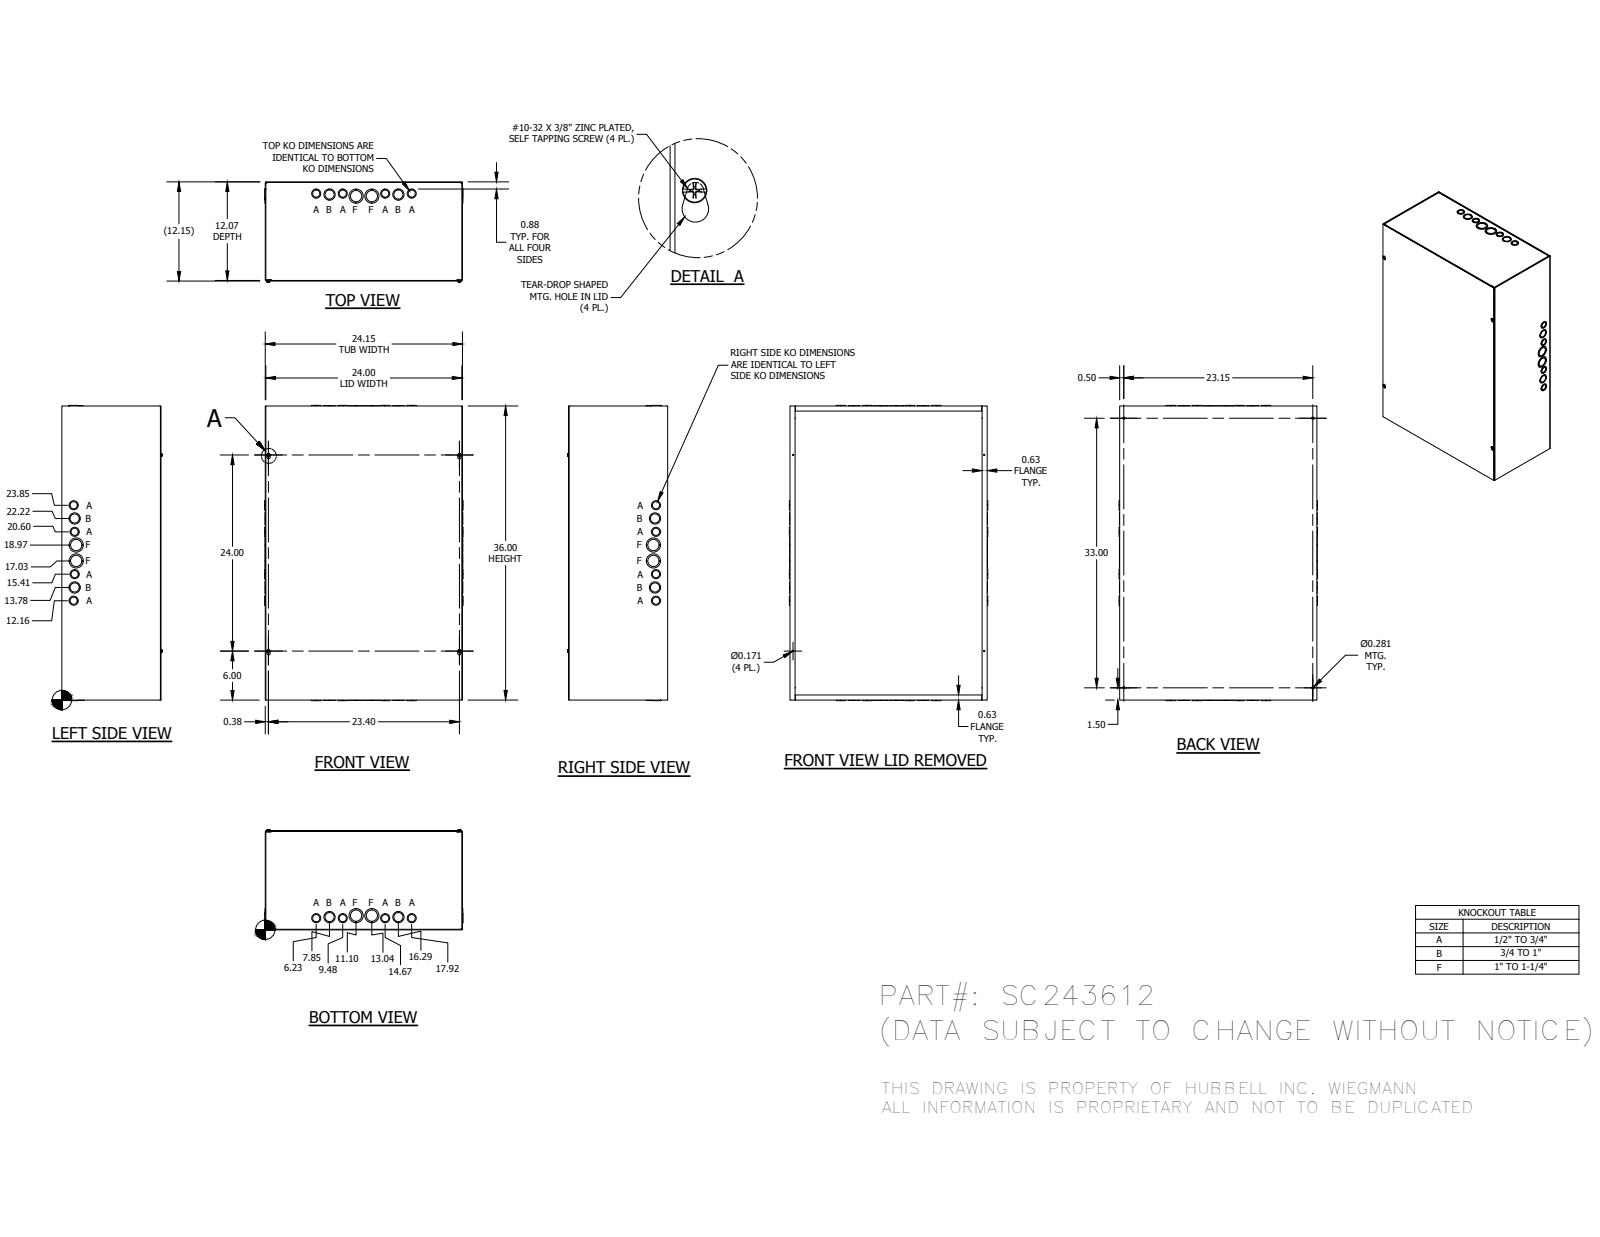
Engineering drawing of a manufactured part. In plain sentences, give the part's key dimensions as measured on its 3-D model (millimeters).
The part is named "SC243612BLR; SC2412TB; SC2436LPA; 37214 (+1 more)". Its 3-D file was written by "Autodesk Inventor 2014 (AUTOMOTIVE_DESIGN)". It is 37 solids with 1219 faces: 899 planar, 236 cylindrical and 84 other. Overall it measures 918.16 by 617.12 by 311.91 millimeters. Round holes: 14 of diameter 28.57, 10 of diameter 22.22, 8 of diameter 34.92, 4 of diameter 4.34, 4 of diameter 7.14, 4 of diameter 44.45. Round bosses or shafts: 4 of diameter 4.83. Partial cylindrical surfaces (rounded edges, fillets, slot ends): 12 of radius 0.4, 12 of radius 2.28, 4 of radius 3.17, 4 of radius 5.16. The main face-to-face distances are 1.88, 306.68, 304.8, 308.56, 611.48, 912.52, 609.6, 613.36, 914.4, 910.64. The hole center spacings are 41.39, 41.4, 42.03, 82.55, 82.69, 90.9, 114.34, 124.07.
